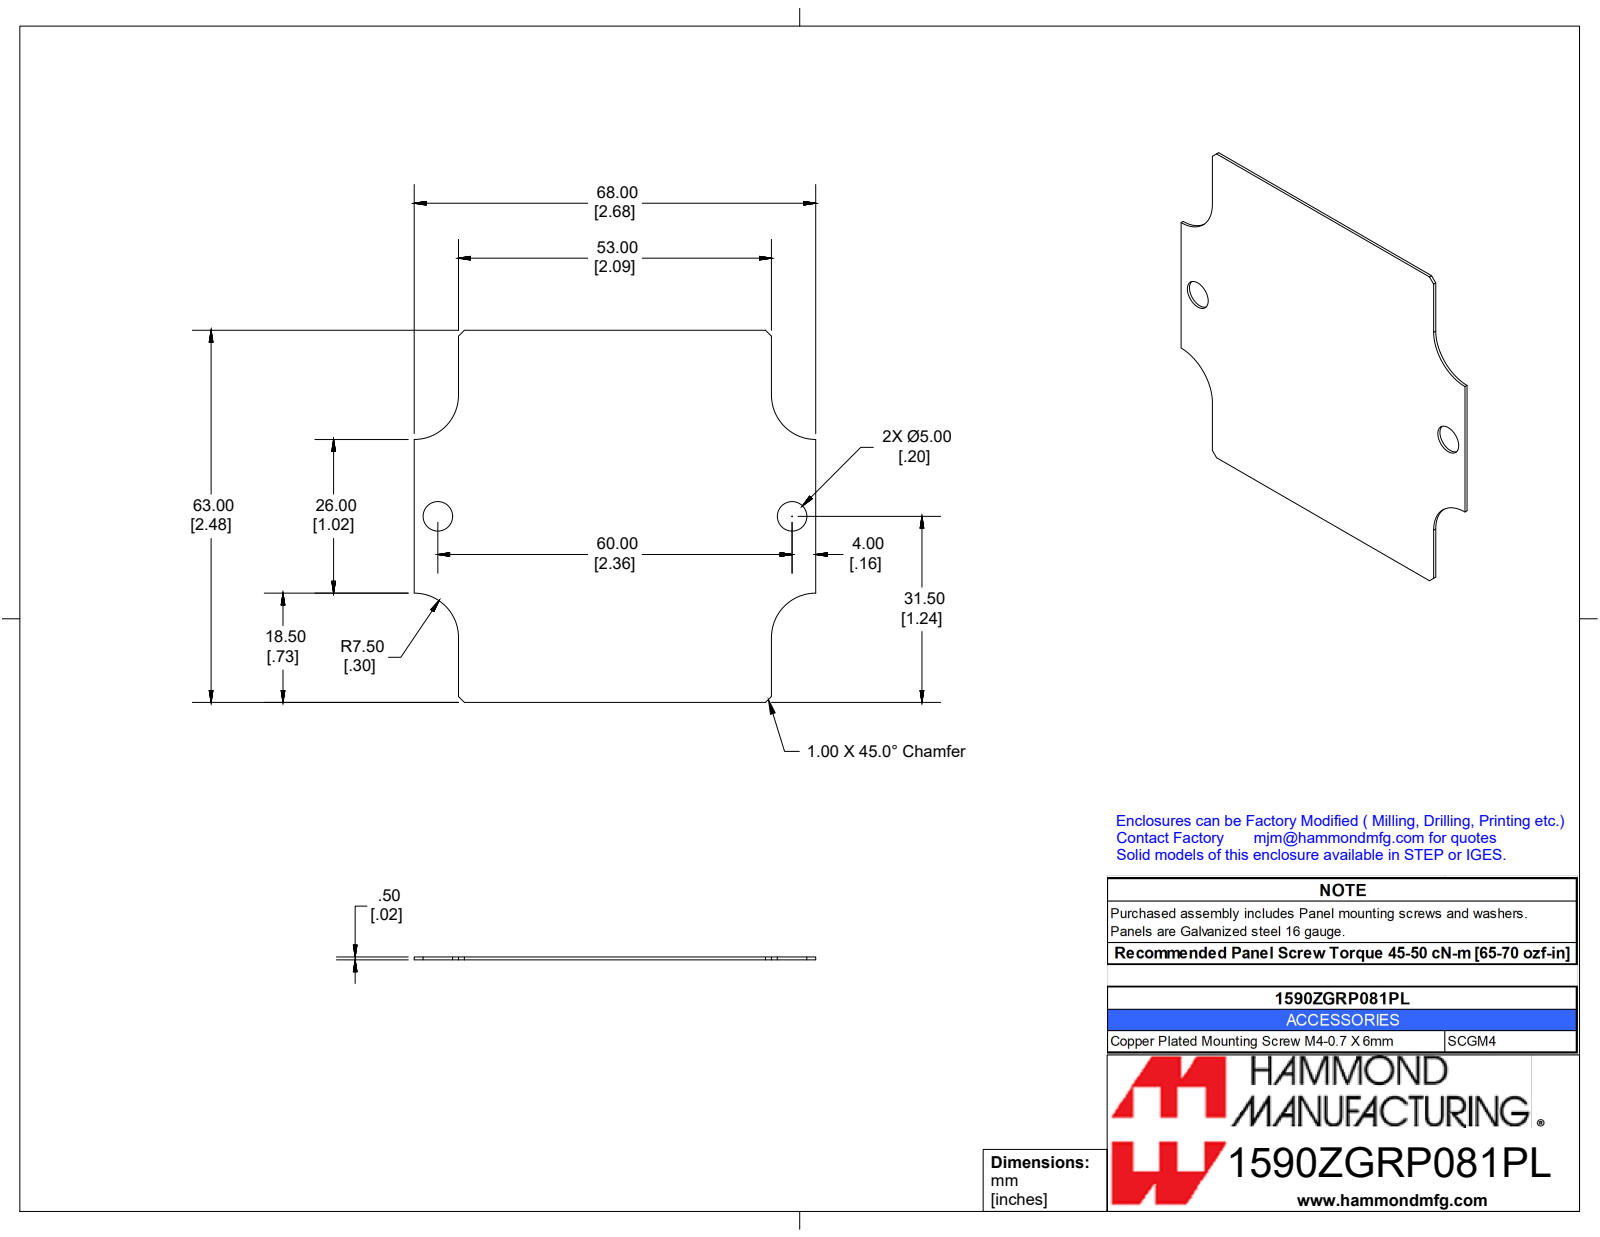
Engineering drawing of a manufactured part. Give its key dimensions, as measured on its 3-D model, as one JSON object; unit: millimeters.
{"part_name": "1590ZGRP081PL", "step_written_by": "SolidWorks 2019 (CONFIG_CONTROL_DESIGN)", "units": "millimeters", "bodies": {"solids": 1, "faces": 20, "planar": 14, "cylindrical": 6, "other": 0}, "overall_size": [68, 63, 0.5], "volume_mm3": 1870, "surface_area_mm2": 7613, "round_holes": [[5, 2]], "partial_cylinders_radius": [[7.5, 4]], "face_to_face_distances": [0.5, 63, 7.5, 60.5, 68, 53, 80.6], "hole_center_spacings": [60]}
